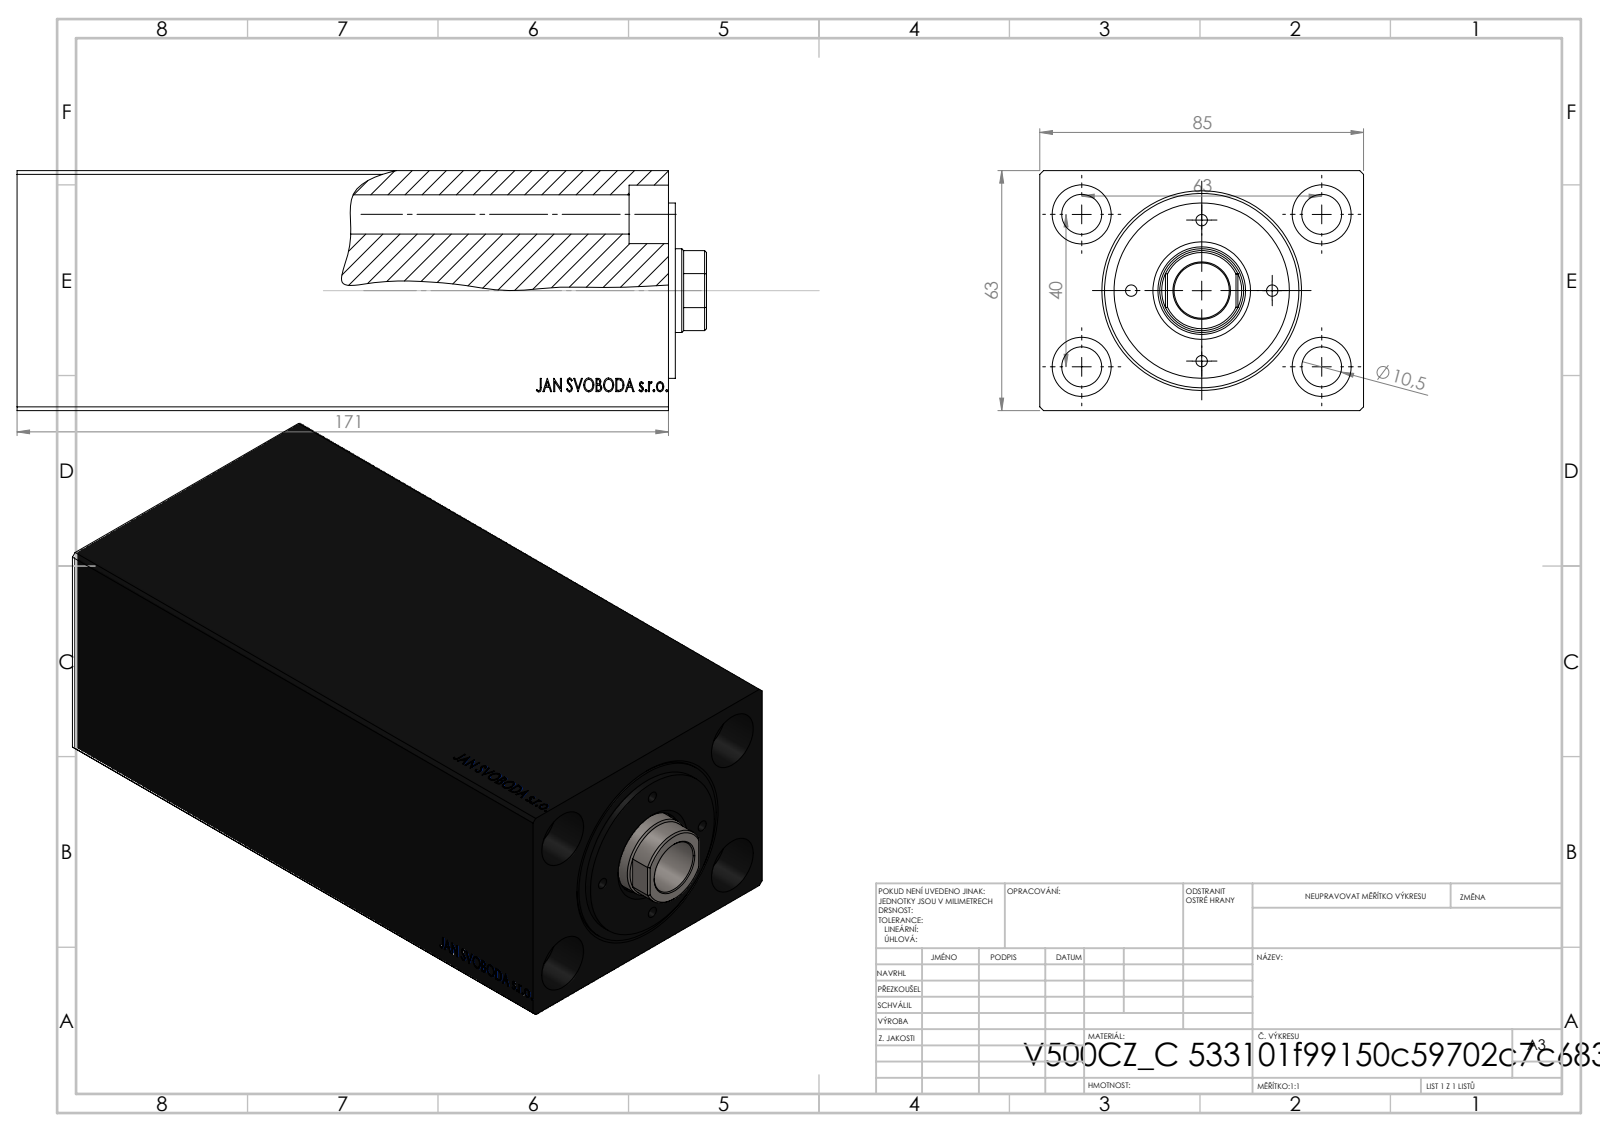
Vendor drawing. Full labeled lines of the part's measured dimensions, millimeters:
STEP written by: SolidWorks 2019 (CONFIG_CONTROL_DESIGN)
Units: millimetres
Bodies: 1 solid, 825 faces (397 planar, 46 cylindrical, 382 other)
Overall size (bounding box): 171 × 85 × 63
Volume: 639 578 mm³ · Surface area: 105 568 mm²
Round holes (diameter × count): ⌀10.5 ×4, ⌀15.5 ×4, ⌀5.5 ×2, ⌀8 ×2, ⌀13.6 ×2, ⌀20 ×2, ⌀36 ×1, ⌀40 ×1, ⌀51 ×1
Main face-to-face distances: 63, 85, 171, 155.7, 15.3, 170.8, 15.1, 10.33, 160.67, 10
Hole centre spacings: 37.31, 40, 63, 74.63, 111.5, 131.5
